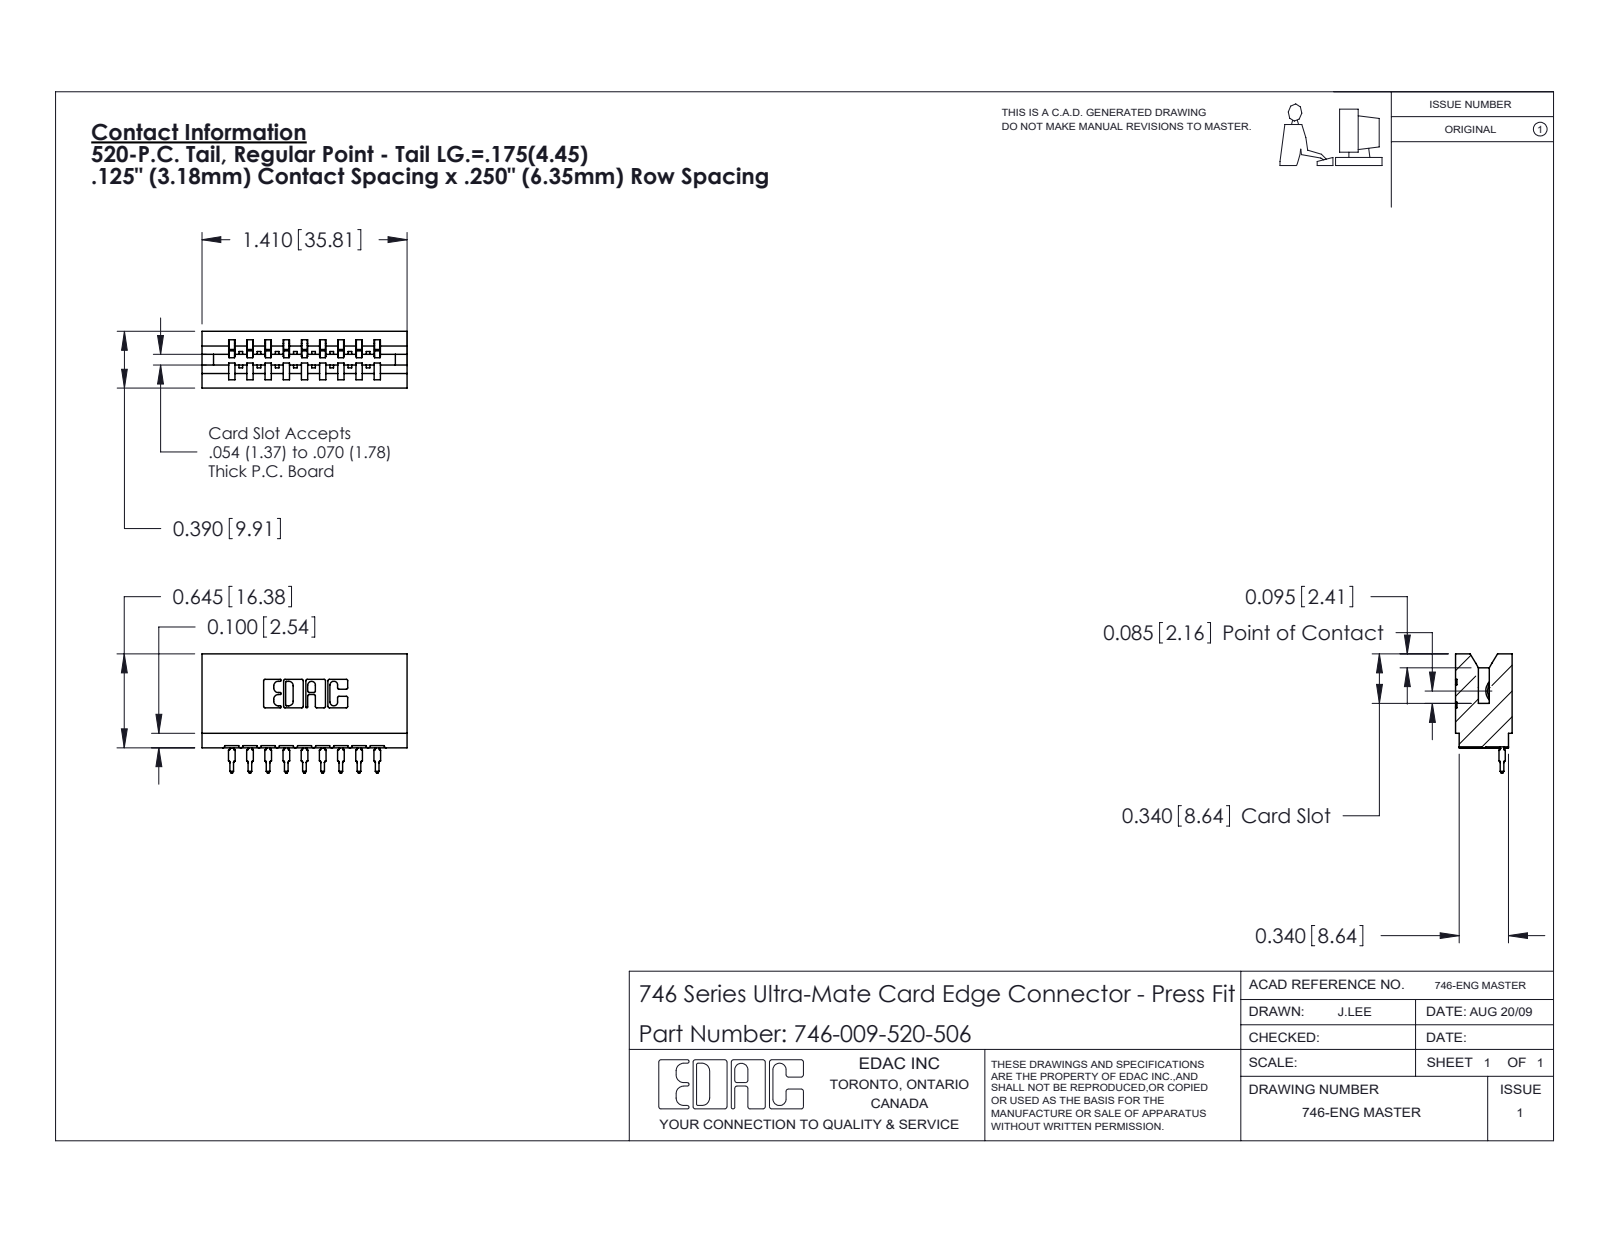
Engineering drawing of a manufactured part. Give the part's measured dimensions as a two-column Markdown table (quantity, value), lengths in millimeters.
| quantity | value |
| --- | --- |
| part name | 746 Part_.340 Slot Depth - 06; 746-292-001_520; 746-009-520-506 |
| STEP written by | SolidWorks 2020 (CONFIG_CONTROL_DESIGN) |
| units | millimeters |
| bodies | 10 solids, 1070 faces (623 planar, 213 cylindrical, 234 other) |
| overall size | 35.8 × 20.8 × 9.9 |
| volume | 4 180 mm³ |
| surface area | 5 087 mm² |
| partial cylindrical surfaces (radius × count) | 0.3 × 22, 0.5 × 18, 0.4 × 10, 0.2 × 6, 0.8 × 6, 0.1 × 4, 0.3 × 4, 0.7 × 3 |
| main face-to-face distances | 6.4, 12.7, 1.1, 8.5, 3.2, 3.2, 7.4, 5.3, 1.4, 9.5 |
